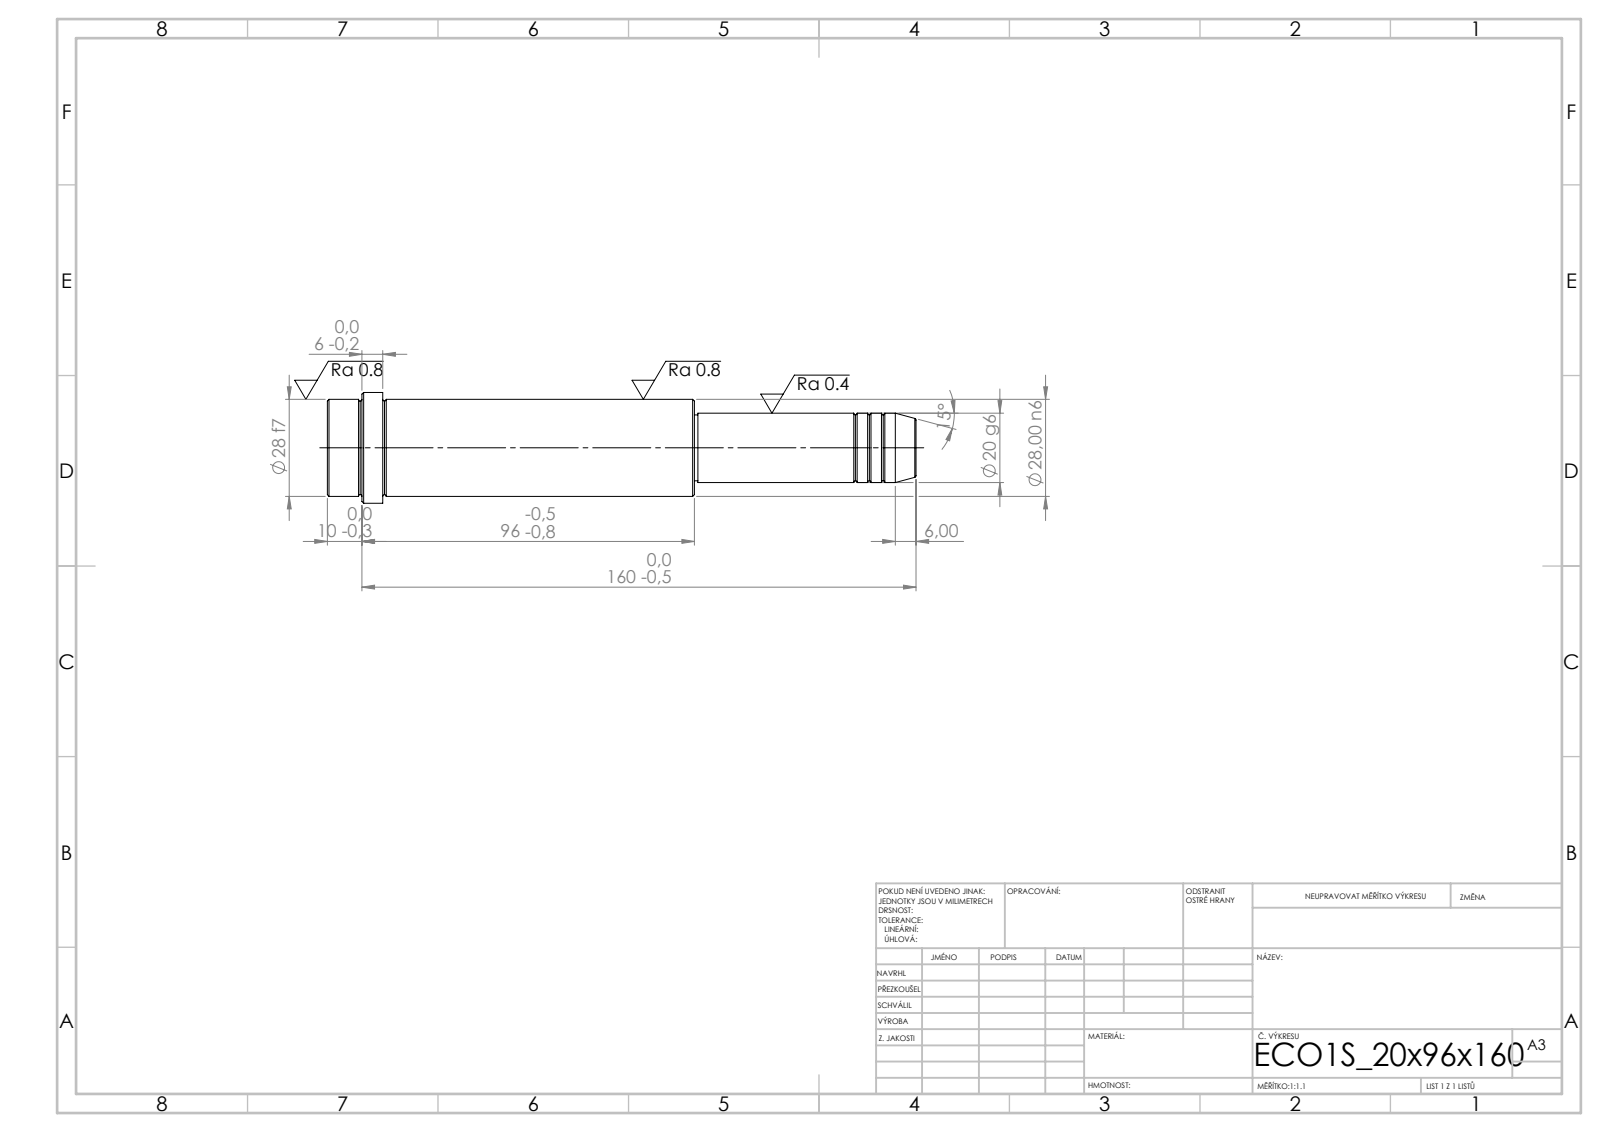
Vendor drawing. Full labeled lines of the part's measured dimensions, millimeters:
STEP written by: SolidWorks 2019 (CONFIG_CONTROL_DESIGN)
Units: millimetres
Bodies: 1 solid, 52 faces (6 planar, 16 cylindrical, 30 other)
Overall size (bounding box): 170 × 32 × 32
Volume: 86 013 mm³ · Surface area: 15 081 mm²
Round bosses / shafts (diameter × count): ⌀32 ×1, ⌀28 ×1, ⌀20 ×1, ⌀19 ×1
Main face-to-face distances: 106, 64, 170, 154, 90, 16, 160, 96, 6, 10
